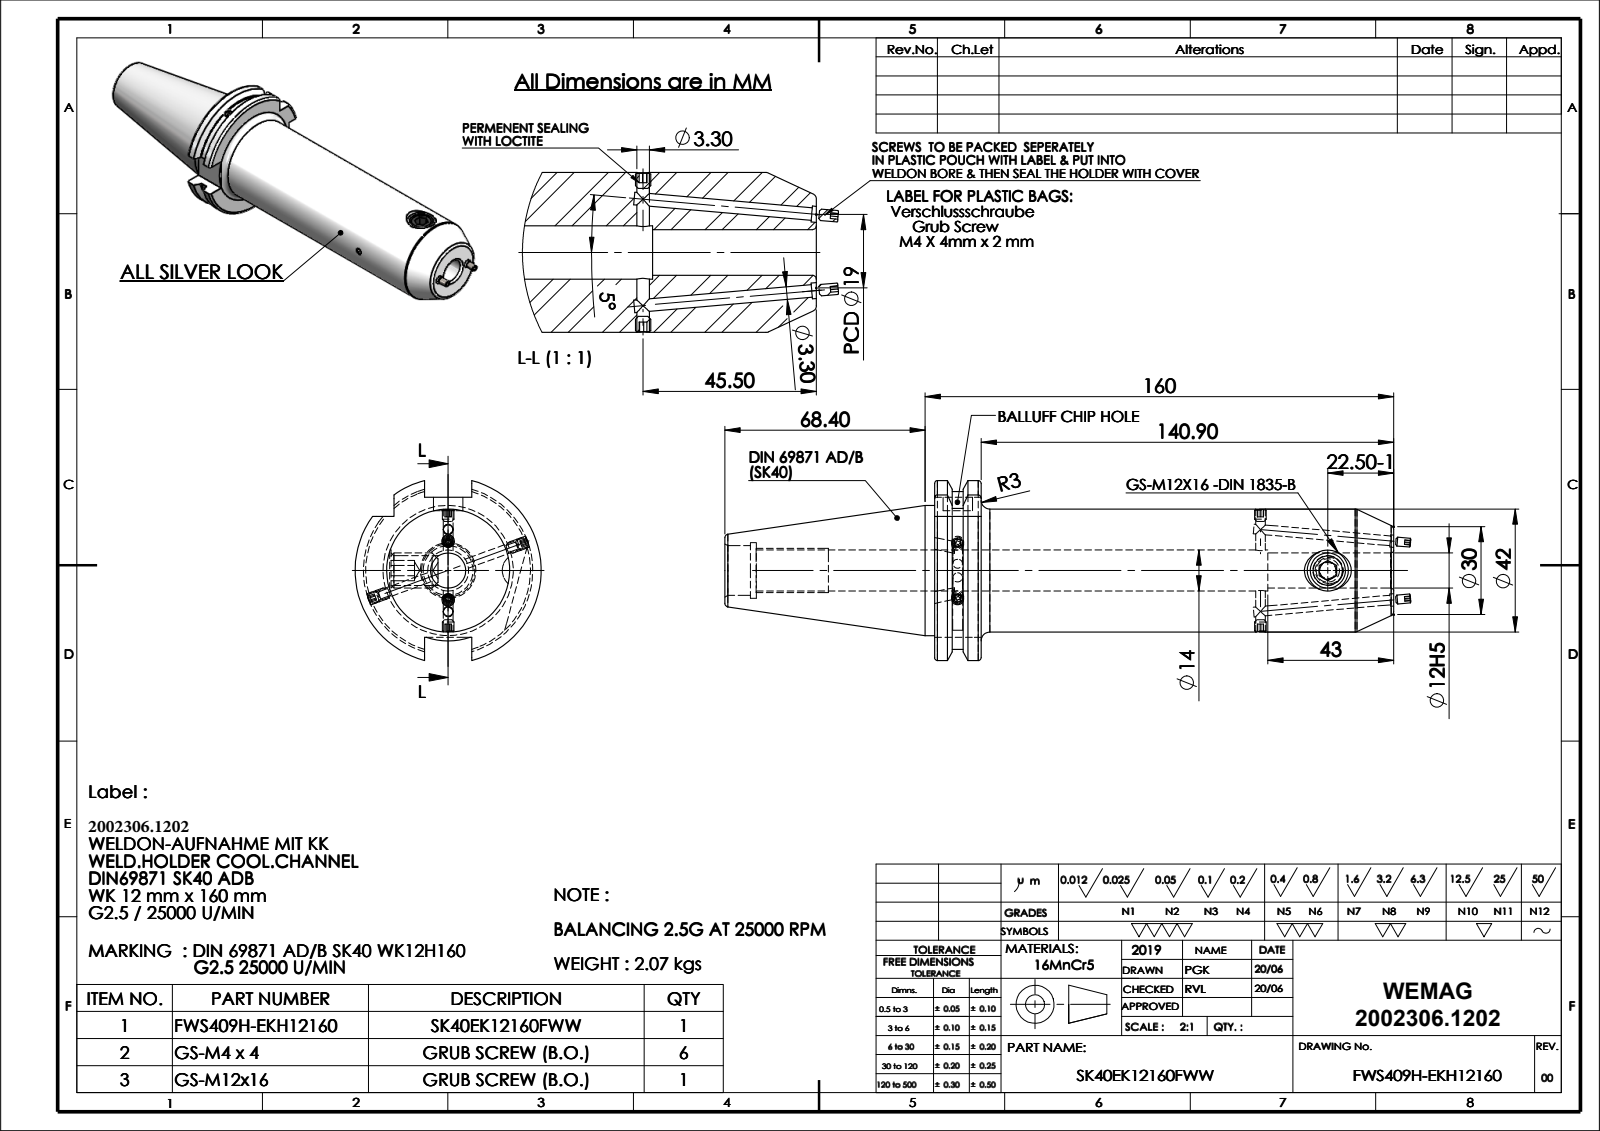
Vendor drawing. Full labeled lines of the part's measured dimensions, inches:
Part name (STEP PRODUCT): 91406-WK212160
STEP written by: SolidWorks 2018 (CONFIG_CONTROL_DESIGN)
Units: inches
Bodies: 1 solid, 131 faces (35 planar, 54 cylindrical, 42 other)
Overall size (bounding box): 8.992 × 2.502 × 2.42
Volume: 16.28 in³ · Surface area: 71.94 in²
Round holes (diameter × count): ⌀0.13 ×4, ⌀0.165 ×2, ⌀0.551 ×2, ⌀0.394 ×1, ⌀0.402 ×1, ⌀0.472 ×1, ⌀0.669 ×1, ⌀0.748 ×1
Round bosses / shafts (diameter × count): ⌀1.75 ×1, ⌀1.654 ×1
Partial cylindrical surfaces — rounded edges, fillets, slot ends (radius × count): R1.107 ×1, R1.251 ×1
Main face-to-face distances: 0.626, 6.173, 5.547, 0.634, 1.882, 2.819, 3.445, 8.992, 0.421, 2.398
Hole centre spacings: 4.069
